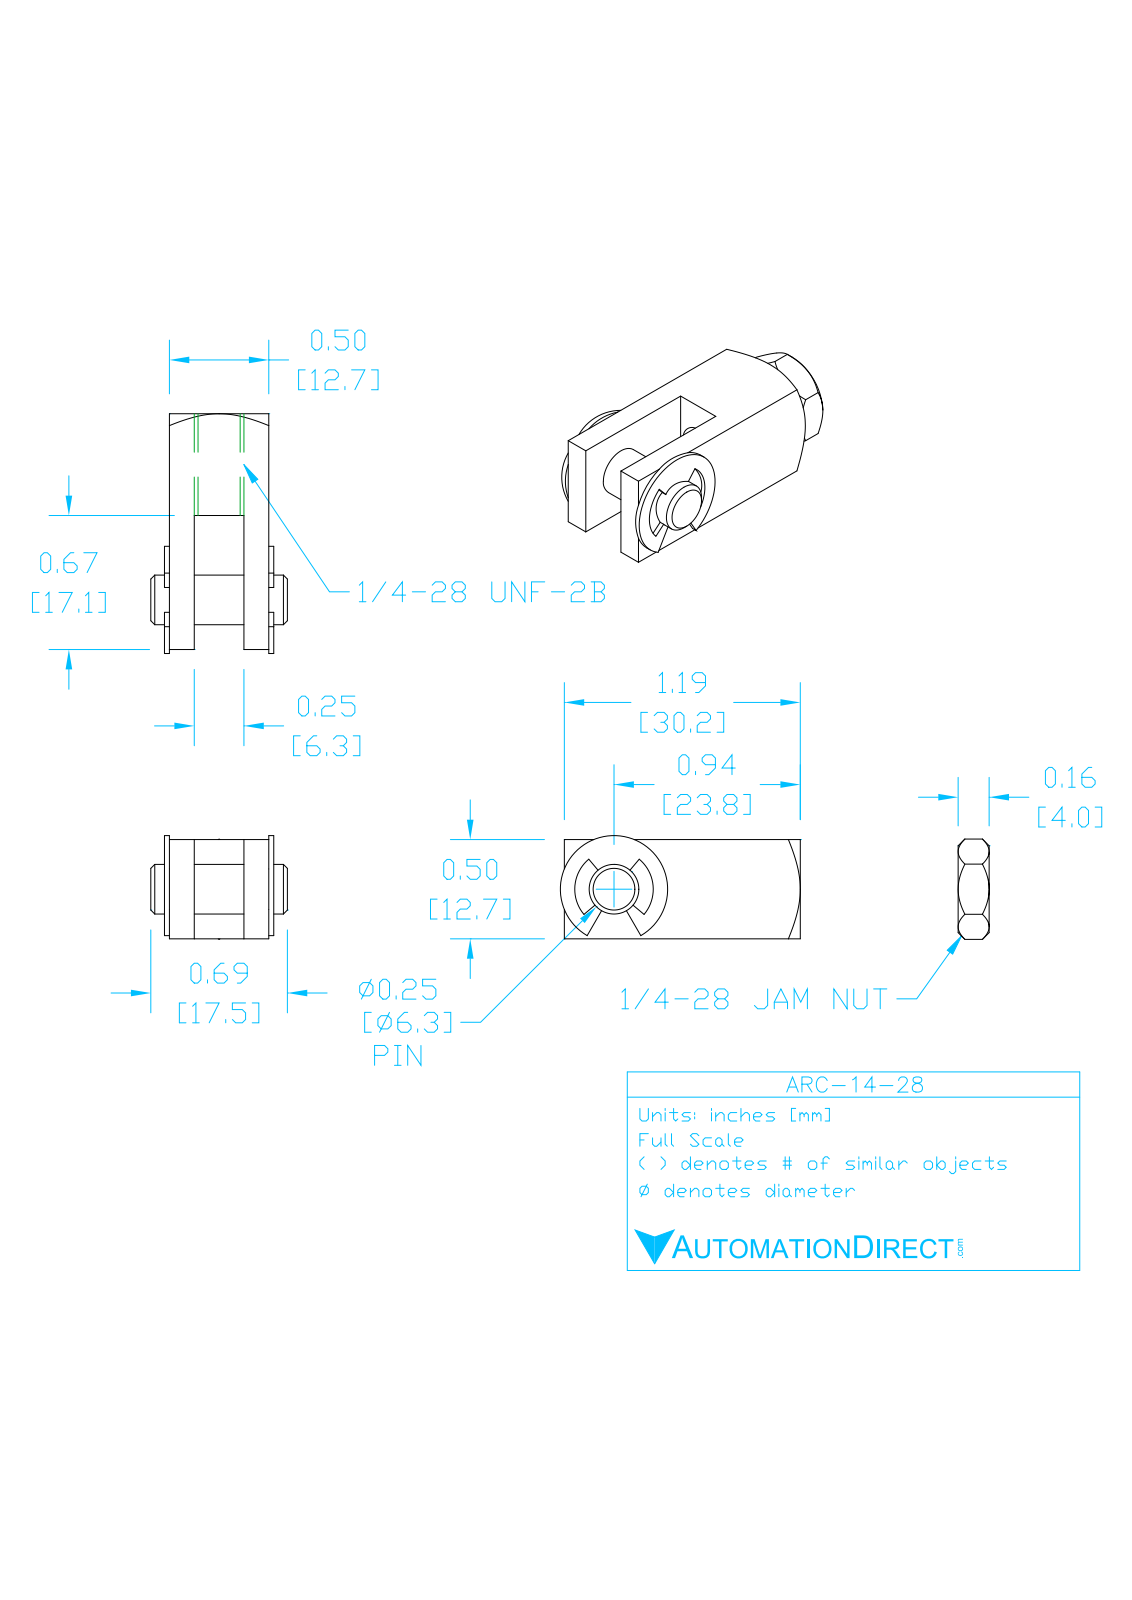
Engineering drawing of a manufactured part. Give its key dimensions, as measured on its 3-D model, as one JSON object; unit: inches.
{"part_name": "ARC-14-28", "step_written_by": "SolidWorks 2017 (AUTOMOTIVE_DESIGN)", "units": "inches", "bodies": {"solids": 5, "faces": 140, "planar": 41, "cylindrical": 64, "other": 35}, "overall_size": [1.348, 0.69, 0.508], "volume_in3": 0.238, "surface_area_in2": 5.308, "round_holes": [[0.211, 1], [0.213, 1], [0.251, 1]], "round_bosses_or_shafts": [[0.25, 1], [0.21, 1]], "partial_cylinders_radius": [[0.021, 6], [0.024, 4], [0.036, 2], [0.105, 1], [0.178, 1], [0.25, 1]], "face_to_face_distances": [0.5, 0.119, 0.381, 0.262, 0.046, 0.548, 0.165, 0.427, 0.546, 0.121]}
